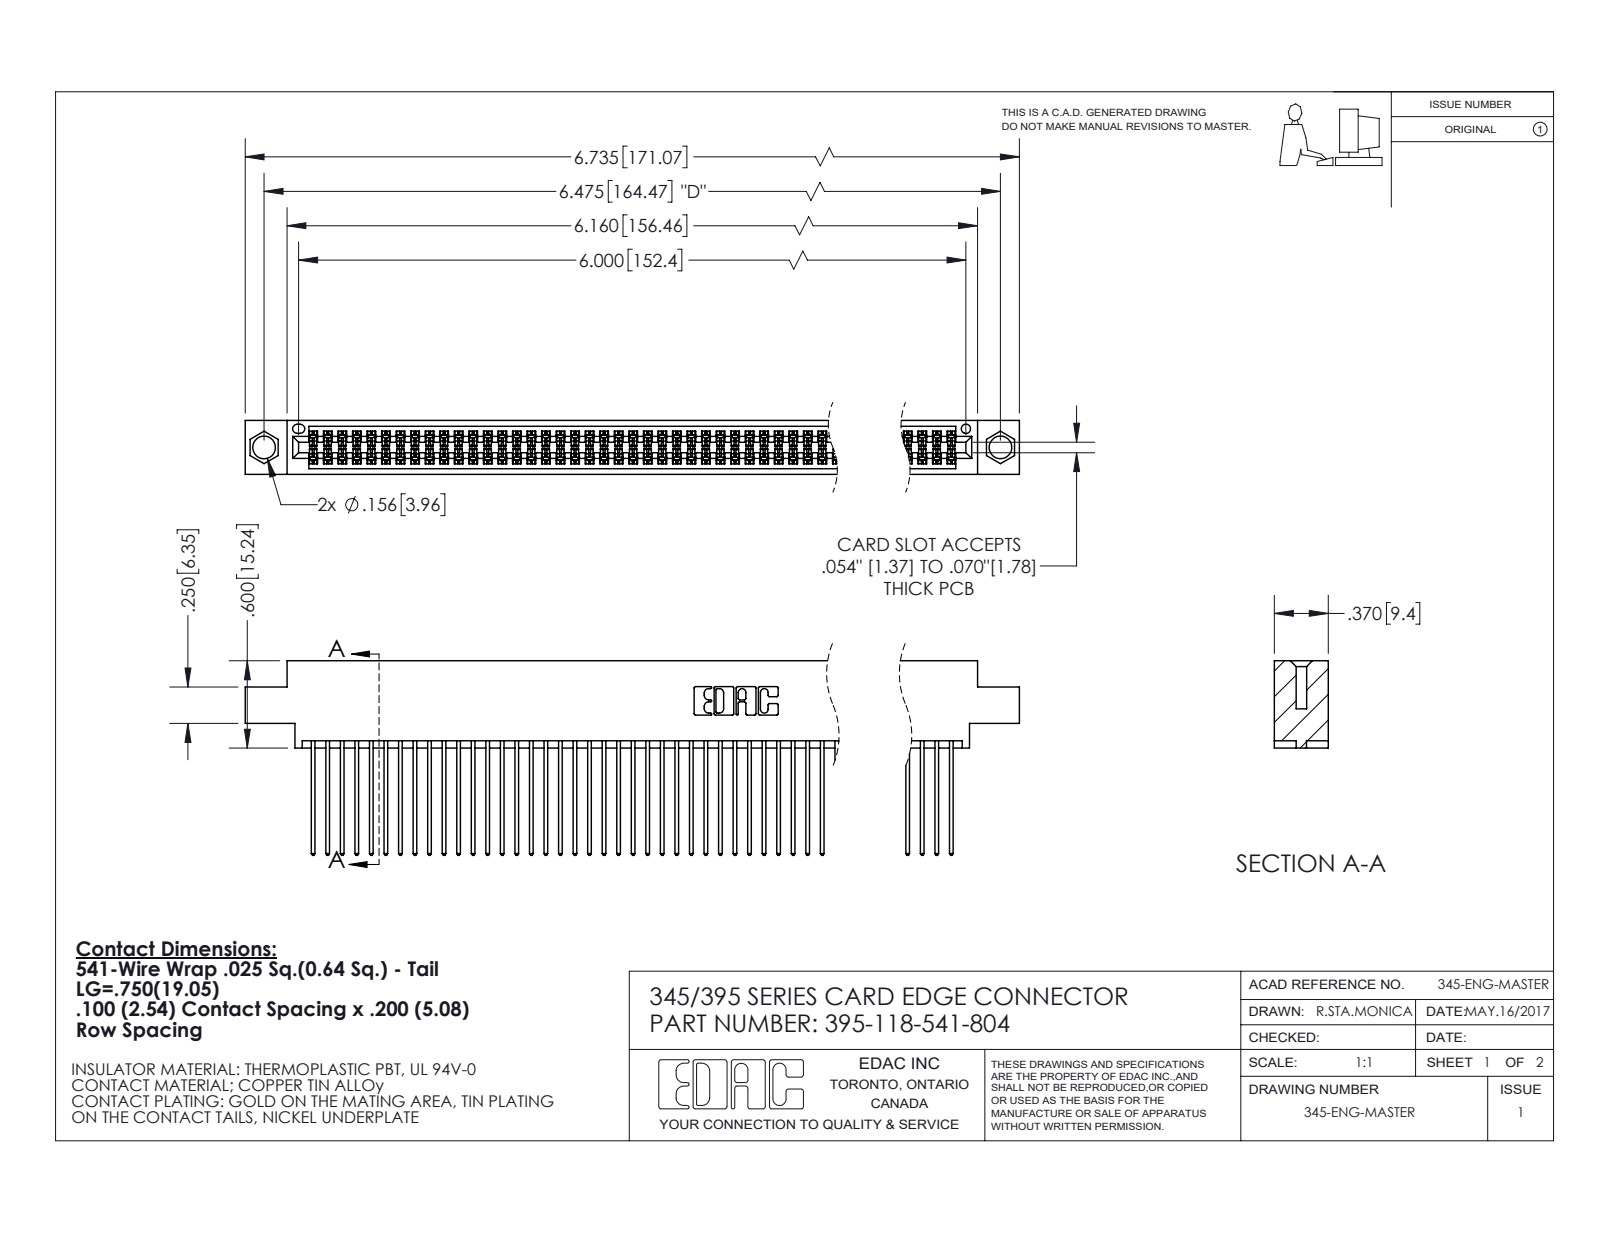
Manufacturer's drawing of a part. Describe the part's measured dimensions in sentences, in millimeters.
The part is named "345 Part_0.170 Offset - 0.156 Dia-TI; 345-292-001_345-293-141; 395-118-541-804". Its 3-D file was written by "SolidWorks 2020 (CONFIG_CONTROL_DESIGN)". It is 119 solids with 6044 faces: 3992 planar, 2052 cylindrical and 0 other. Overall it measures 171.1 by 34 by 9.4 millimeters. Its volume is 17 240 cubic millimeters and its surface area 28 980 square millimeters. Round holes: 2 of diameter 4, 1 of diameter 1.6. Partial cylindrical surfaces (rounded edges, fillets, slot ends): 177 of radius 0.2, 118 of radius 0.3, 22 of radius 0.3, 6 of radius 0.2, 6 of radius 0.8, 3 of radius 0.7, 2 of radius 0.4, 2 of radius 0.5. The main face-to-face distances are 1.8, 7.6, 5.1, 2.5, 6.9, 0.6, 5.7, 9.4, 4.4, 3.8. The hole center spacings are 6.9, 158.5, 164.5.
